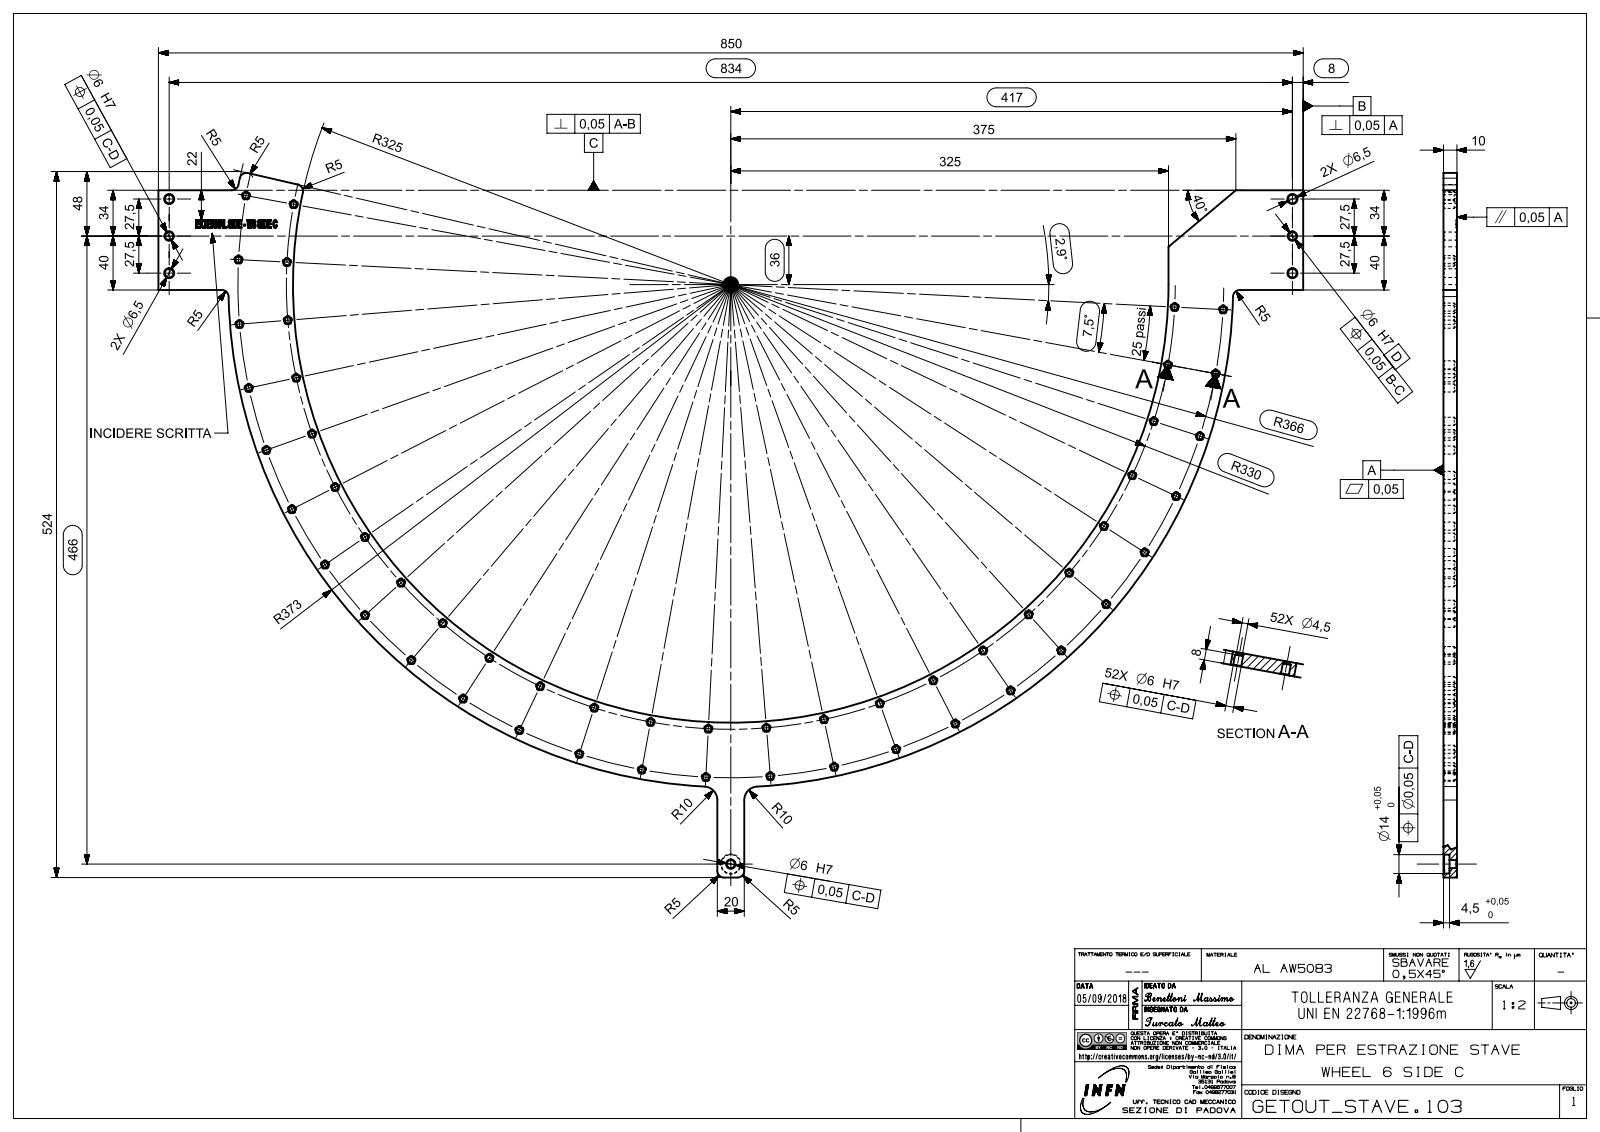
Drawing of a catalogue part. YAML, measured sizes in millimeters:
part_name: "bezA730AE56cd0y"
step_written_by: "SIEMENS PLM Software NX 12.0 (AUTOMOTIVE_DESIGN)"
units: millimeters
bodies: {solids: 1, faces: 500, planar: 220, cylindrical: 125, other: 155}
overall_size: [850, 522.9, 10]
volume: 663139
surface_area: 173190
round_holes:
  - {diameter: 6, count: 55}
  - {diameter: 4.5, count: 52}
  - {diameter: 6.5, count: 4}
  - {diameter: 14, count: 1}
partial_cylinders:
  - {radius: 5, count: 7}
  - {radius: 10, count: 2}
  - {radius: 325, count: 1}
  - {radius: 373, count: 1}
face_to_face_distances: [10, 415, 435, 74, 850, 2, 8, 20, 750, 335]
hole_center_spacings: [140.3, 57.99, 183.46, 97.61, 309.52, 36, 57.98, 97.6]
